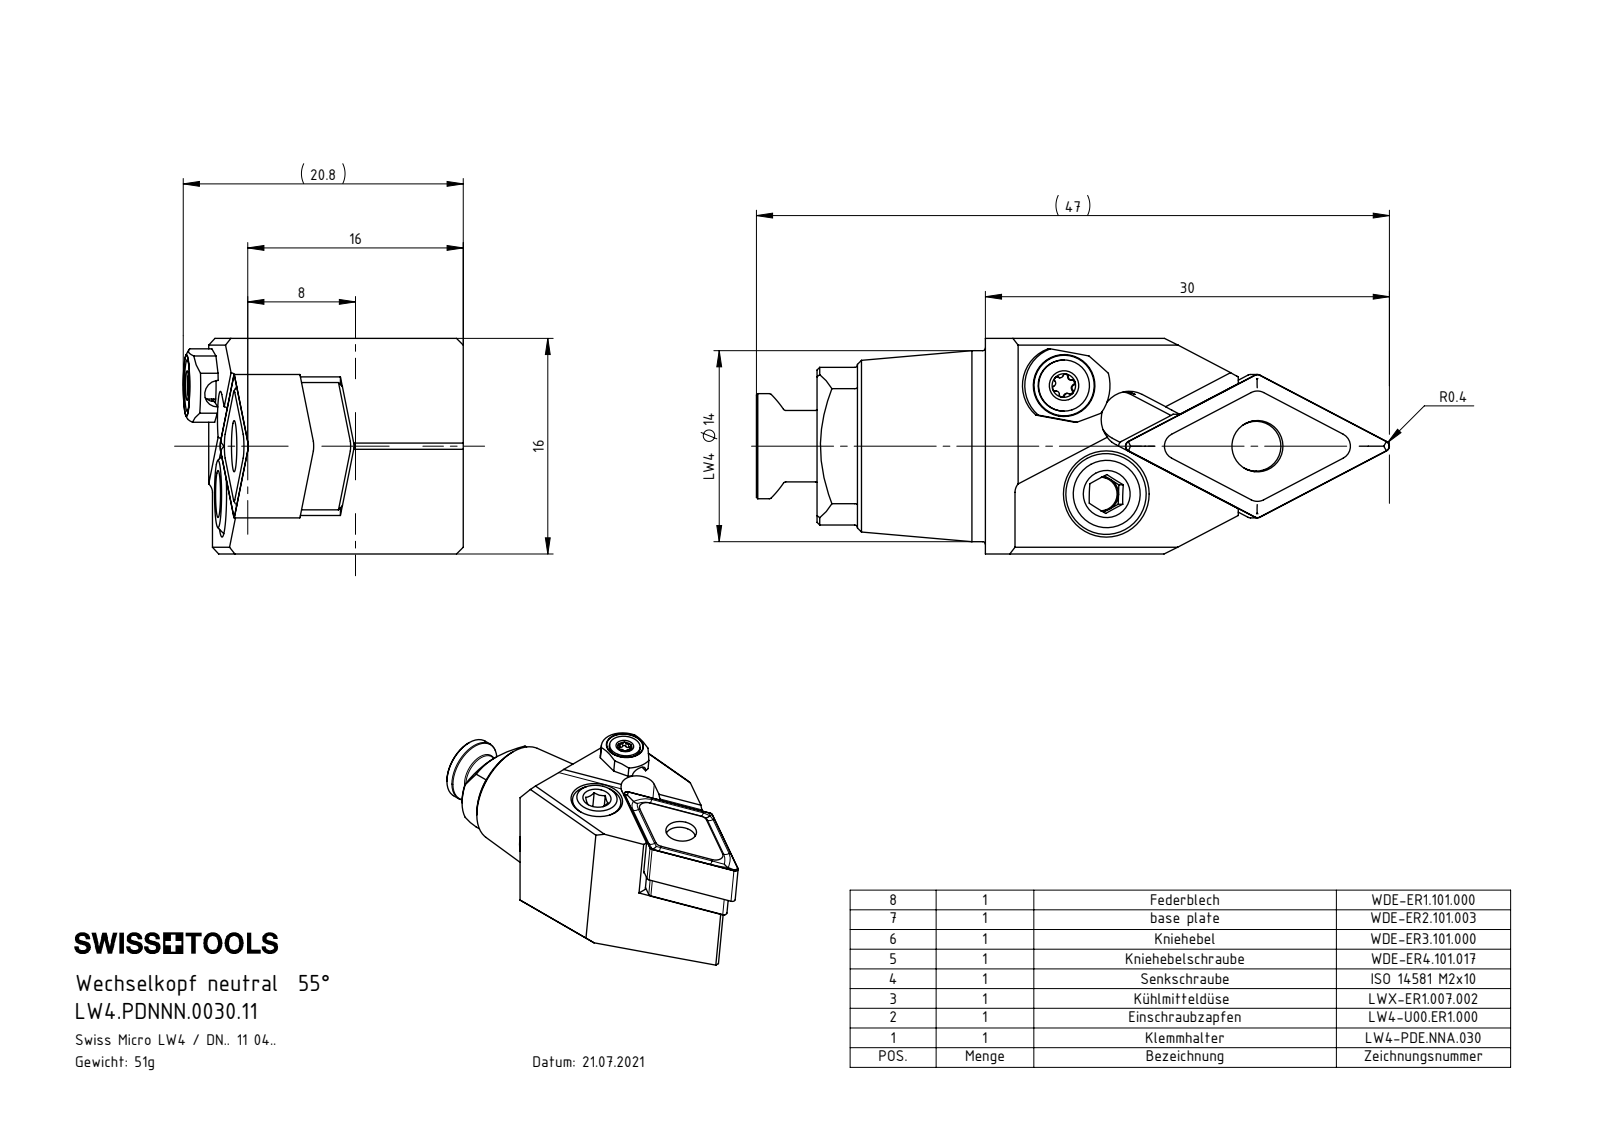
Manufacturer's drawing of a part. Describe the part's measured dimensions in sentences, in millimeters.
The part is named "WDE-ER3.101.000_A; DNMG110404; WDE-ER4.101.017_A; WDE-ER1.101.000 (+4 more)". Its 3-D file was written by "SolidWorks 2022 (CONFIG_CONTROL_DESIGN)". It is 7 solids with 286 faces: 112 planar, 78 cylindrical and 96 other. Overall it measures 42.5 by 20.7 by 16 millimeters. Its volume is 6 571 cubic millimeters and its surface area 4 841 square millimeters. Round holes: 2 of diameter 3, 1 of diameter 1.6, 1 of diameter 2, 1 of diameter 2.5, 1 of diameter 3.81, 1 of diameter 4.8, 1 of diameter 5, 1 of diameter 5.5, 1 of diameter 6.4. Round bosses or shafts: 1 of diameter 14.17, 1 of diameter 6, 1 of diameter 5.9, 1 of diameter 3.8, 1 of diameter 2.87, 1 of diameter 2. Partial cylindrical surfaces (rounded edges, fillets, slot ends): 8 of radius 0.2, 6 of radius 0.24, 4 of radius 0.4, 4 of radius 0.8, 4 of radius 2.1, 1 of radius 0.5, 1 of radius 1.83, 1 of radius 1.85. The main face-to-face distances are 16, 8.68, 9, 0.53, 9.53, 0.85, 4.94, 8.15, 4.63, 0.31. The hole center spacings are 11.8, 8.73, 8.74, 11.79, 11.81, 15.32, 15.33.
